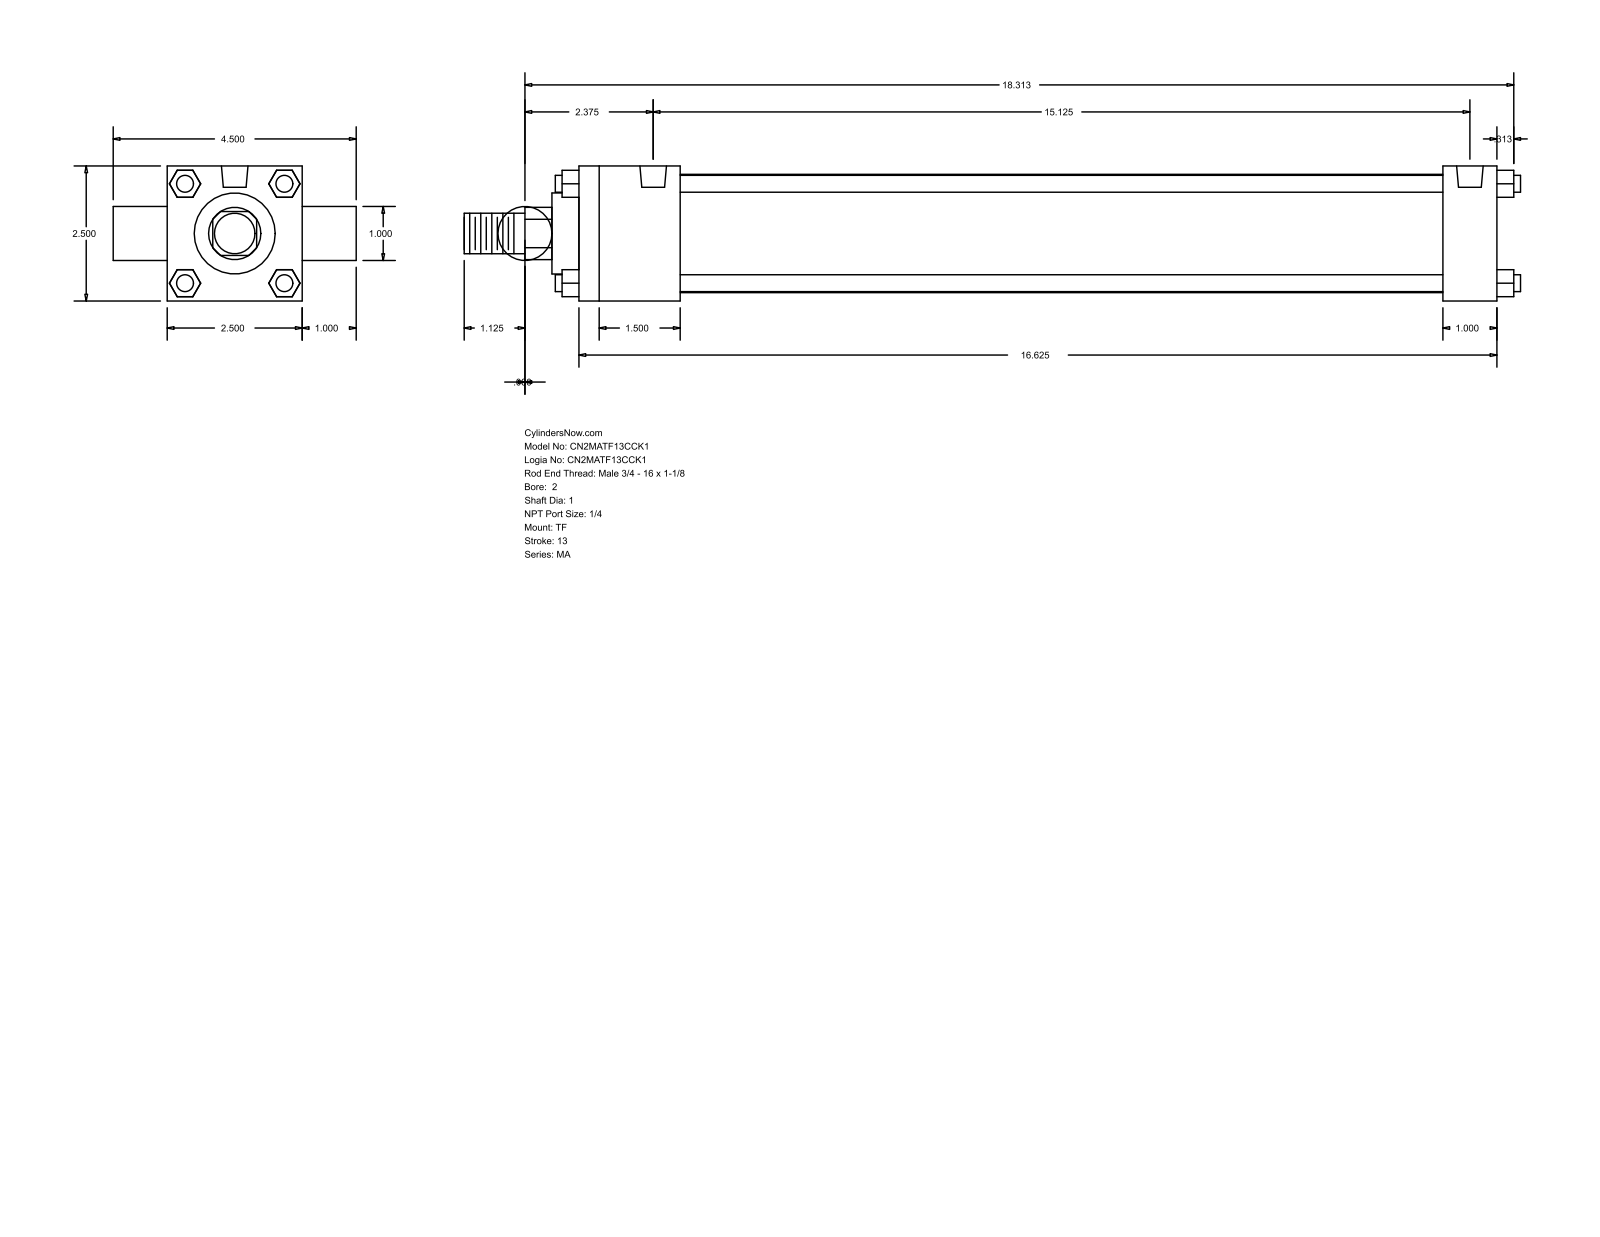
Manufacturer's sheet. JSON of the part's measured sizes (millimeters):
{"part_name": "MA_TF__0200_1", "step_written_by": "GSSL Pune (CONFIG_CONTROL_DESIGN)", "units": "millimeters", "bodies": {"solids": 0, "faces": 120, "planar": 92, "cylindrical": 28, "other": 0}, "overall_size": [496.89, 114.3, 63.5], "round_holes": [[7.94, 3], [12.49, 2]], "round_bosses_or_shafts": [[7.94, 4], [25.4, 2], [55.63, 1], [38.1, 1], [19.05, 1]], "partial_cylinders_radius": [[12.29, 1]], "face_to_face_distances": [63.5, 25.4, 431.8, 12.7, 47.63, 406.4, 358.77, 384.17, 88.9, 40.47], "hole_center_spacings": [384.17]}
